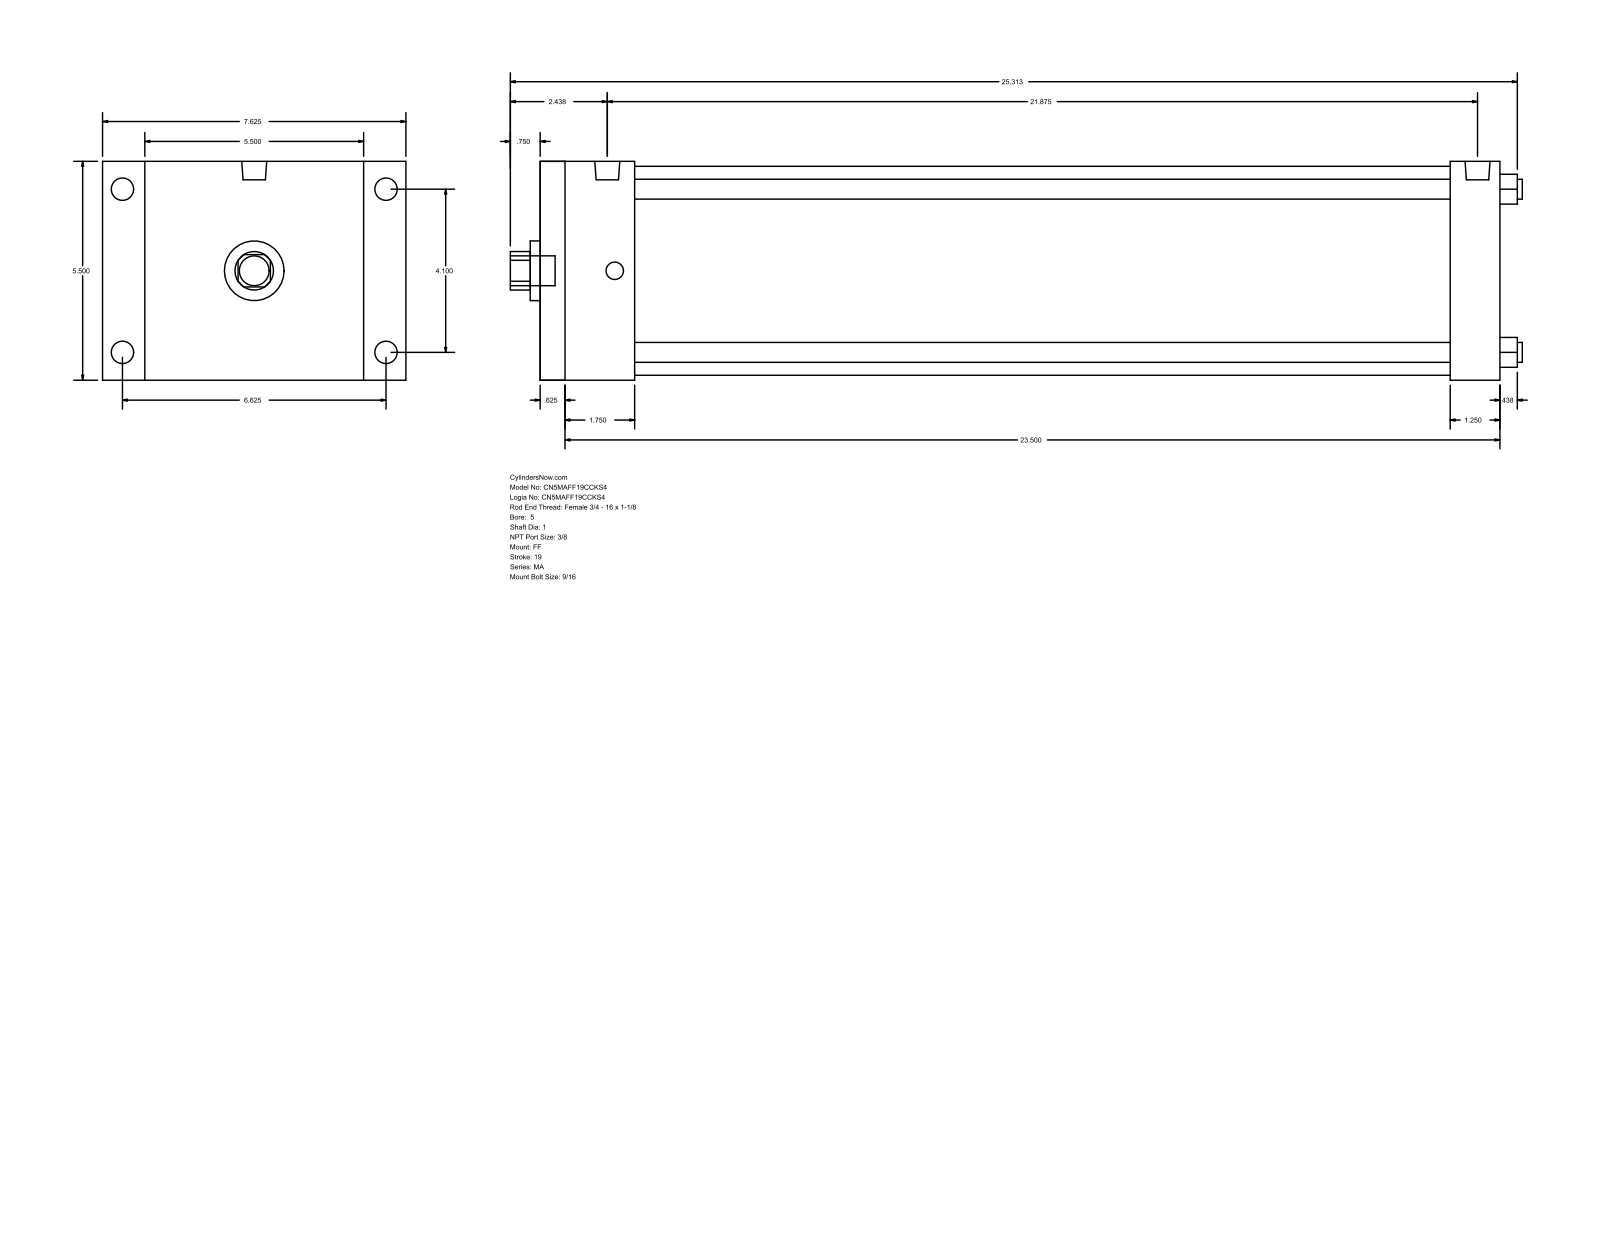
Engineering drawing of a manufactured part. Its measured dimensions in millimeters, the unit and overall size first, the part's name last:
Units: millimetres
Overall size (bounding box): 646.11 × 193.68 × 139.7
Round holes (diameter × count): ⌀12.7 ×4, ⌀25.4 ×1, ⌀38.1 ×1, ⌀133.35 ×1
Round bosses / shafts (diameter × count): ⌀14.29 ×4, ⌀11.11 ×4, ⌀15.93 ×2, ⌀19.05 ×1
Partial cylindrical surfaces — rounded edges, fillets, slot ends (radius × count): R12.29 ×1
Main face-to-face distances: 139.7, 612.78, 15.87, 596.91, 581.03, 565.16, 31.75, 60.33, 44.46, 520.7
Hole centre spacings: 73.64, 104.14, 147.28
Bodies: 0 solids, 92 faces (64 planar, 28 cylindrical, 0 other)
Part name (STEP PRODUCT): MA_FF__0500_1
STEP written by: GSSL Pune (CONFIG_CONTROL_DESIGN)
